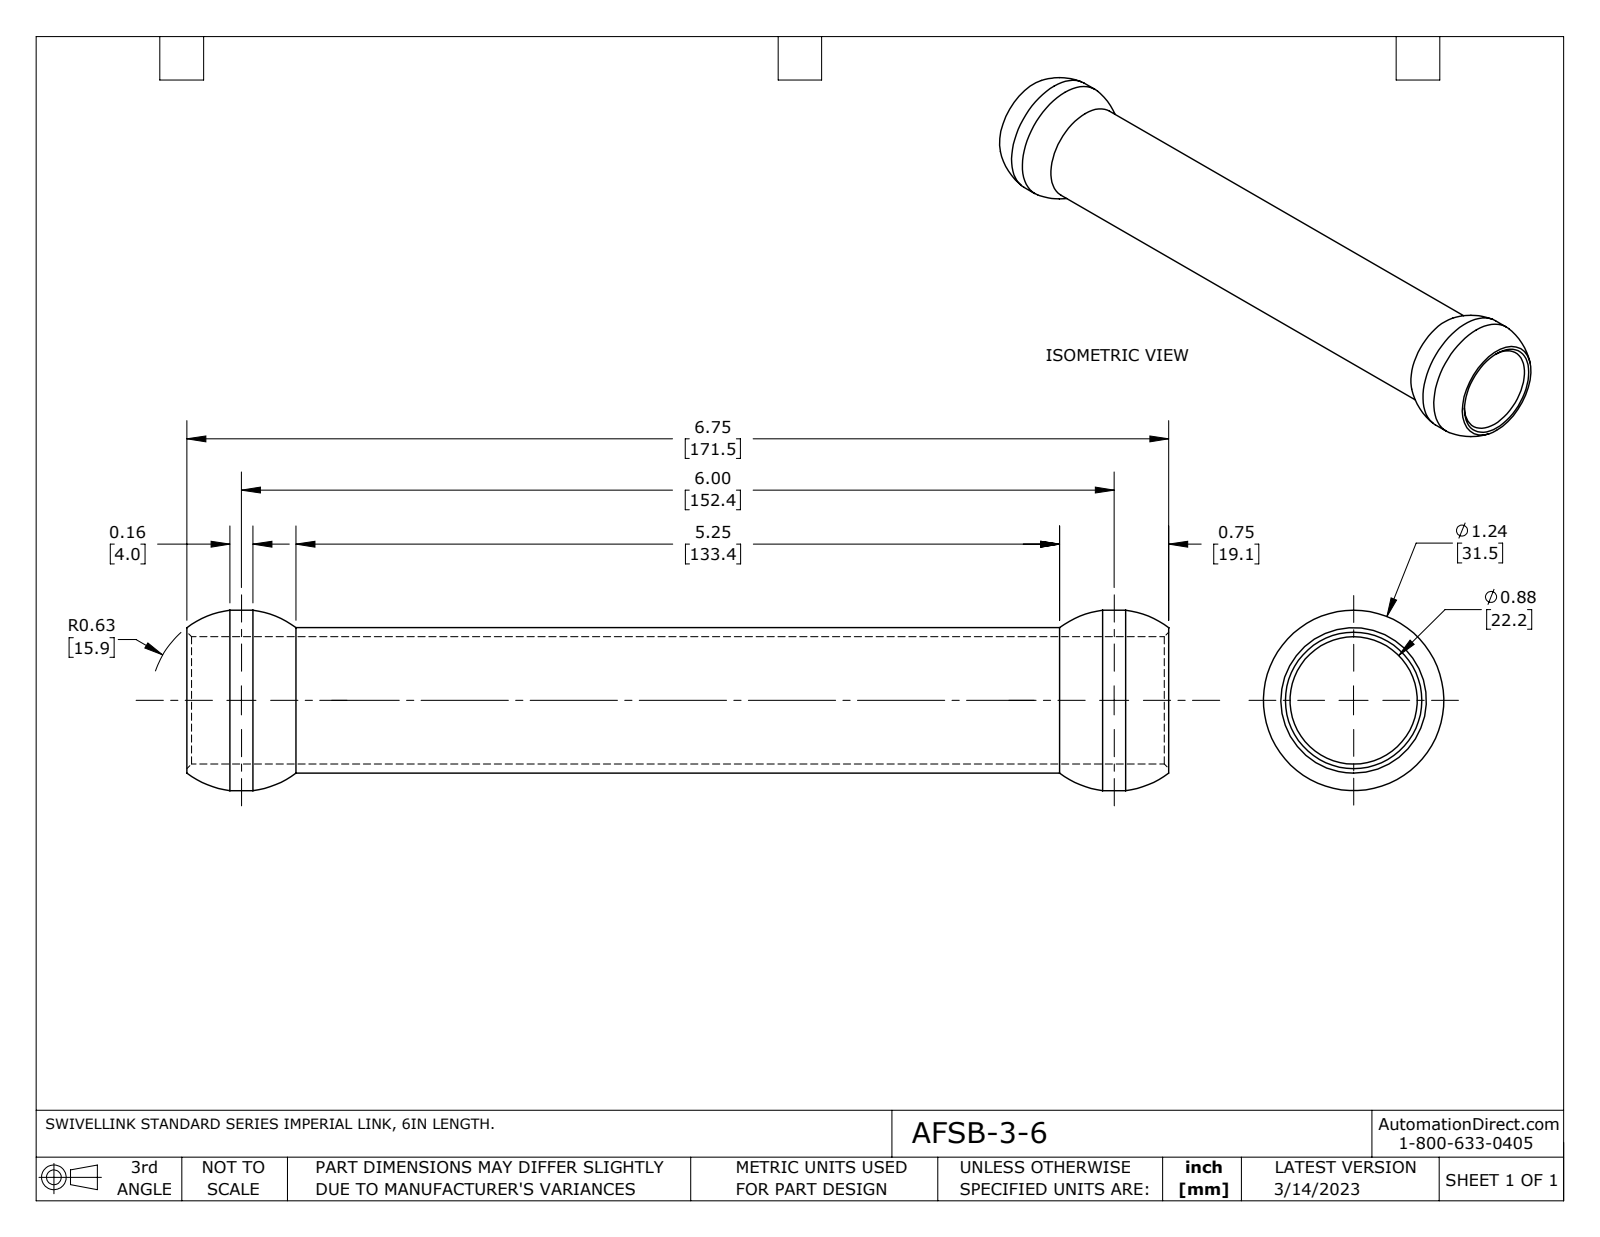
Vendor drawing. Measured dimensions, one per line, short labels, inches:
name: AFSB-3-6
written by: SolidWorks 2021 (AUTOMOTIVE_DESIGN)
unit: in
bodies: 1 solid, 12 faces (2 planar, 4 cylindrical, 6 other)
size: 6.75 × 1.24 × 1.24
volume: 1.673 in³; area: 41.18 in²
holes: 1× ⌀0.875
bosses: 1× ⌀1.24, 1× ⌀1
face distances: 6.75
